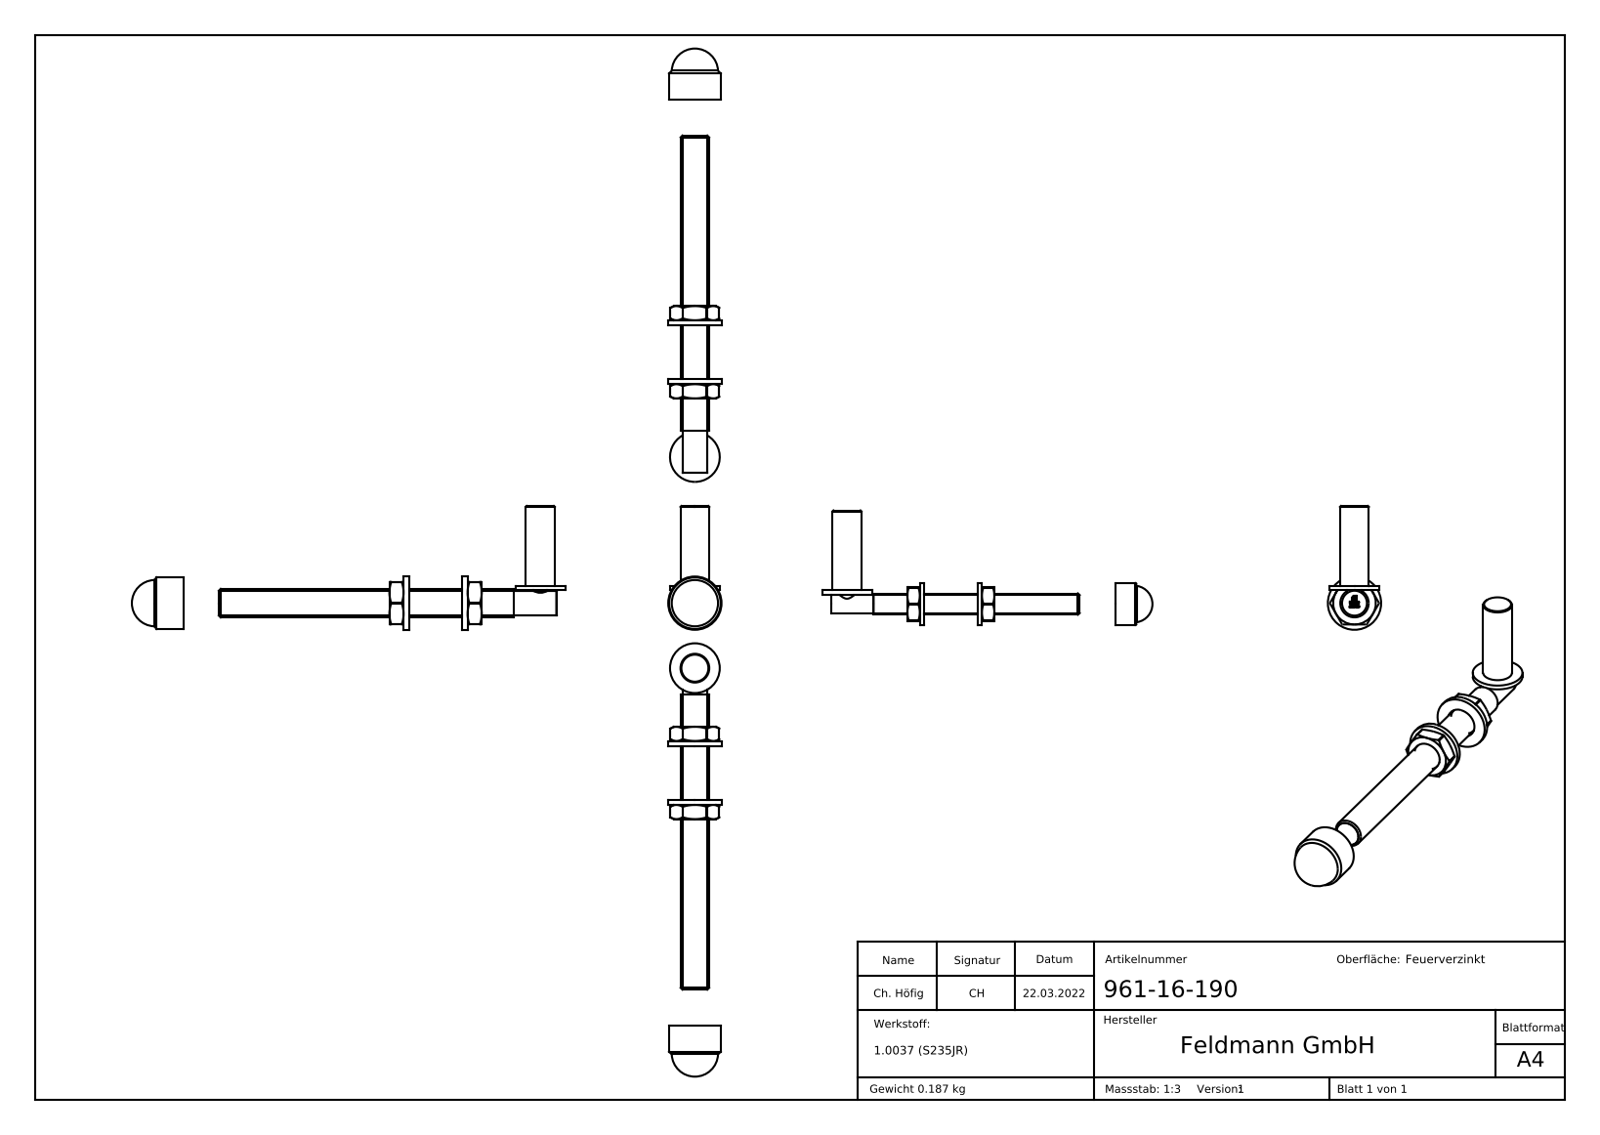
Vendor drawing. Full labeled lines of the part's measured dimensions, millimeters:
Part name (STEP PRODUCT): 961-1X-XXX Teil2_961-16-190 Teil2; DIN 936 M8-M24_DIN 936 M16; 961-16-190; 961-1X-XXX Teil1_961-16-190 Teil1 (+1 more)
STEP written by: SolidWorks 2018 (CONFIG_CONTROL_DESIGN)
Units: millimetres
Bodies: 6 solids, 351 faces (180 planar, 25 cylindrical, 146 other)
Overall size (bounding box): 244 × 69.7 × 30
Volume: 59 872 mm³ · Surface area: 24 489 mm²
Round holes (diameter × count): ⌀14 ×1, ⌀17 ×1, ⌀24 ×1
Round bosses / shafts (diameter × count): ⌀30 ×1, ⌀29 ×1, ⌀28 ×1, ⌀16.2 ×1, ⌀16 ×1, ⌀8 ×1
Partial cylindrical surfaces — rounded edges, fillets, slot ends (radius × count): R0.5 ×6
Main face-to-face distances: 24, 33, 3, 36, 11, 8, 41, 44, 30, 2.5
